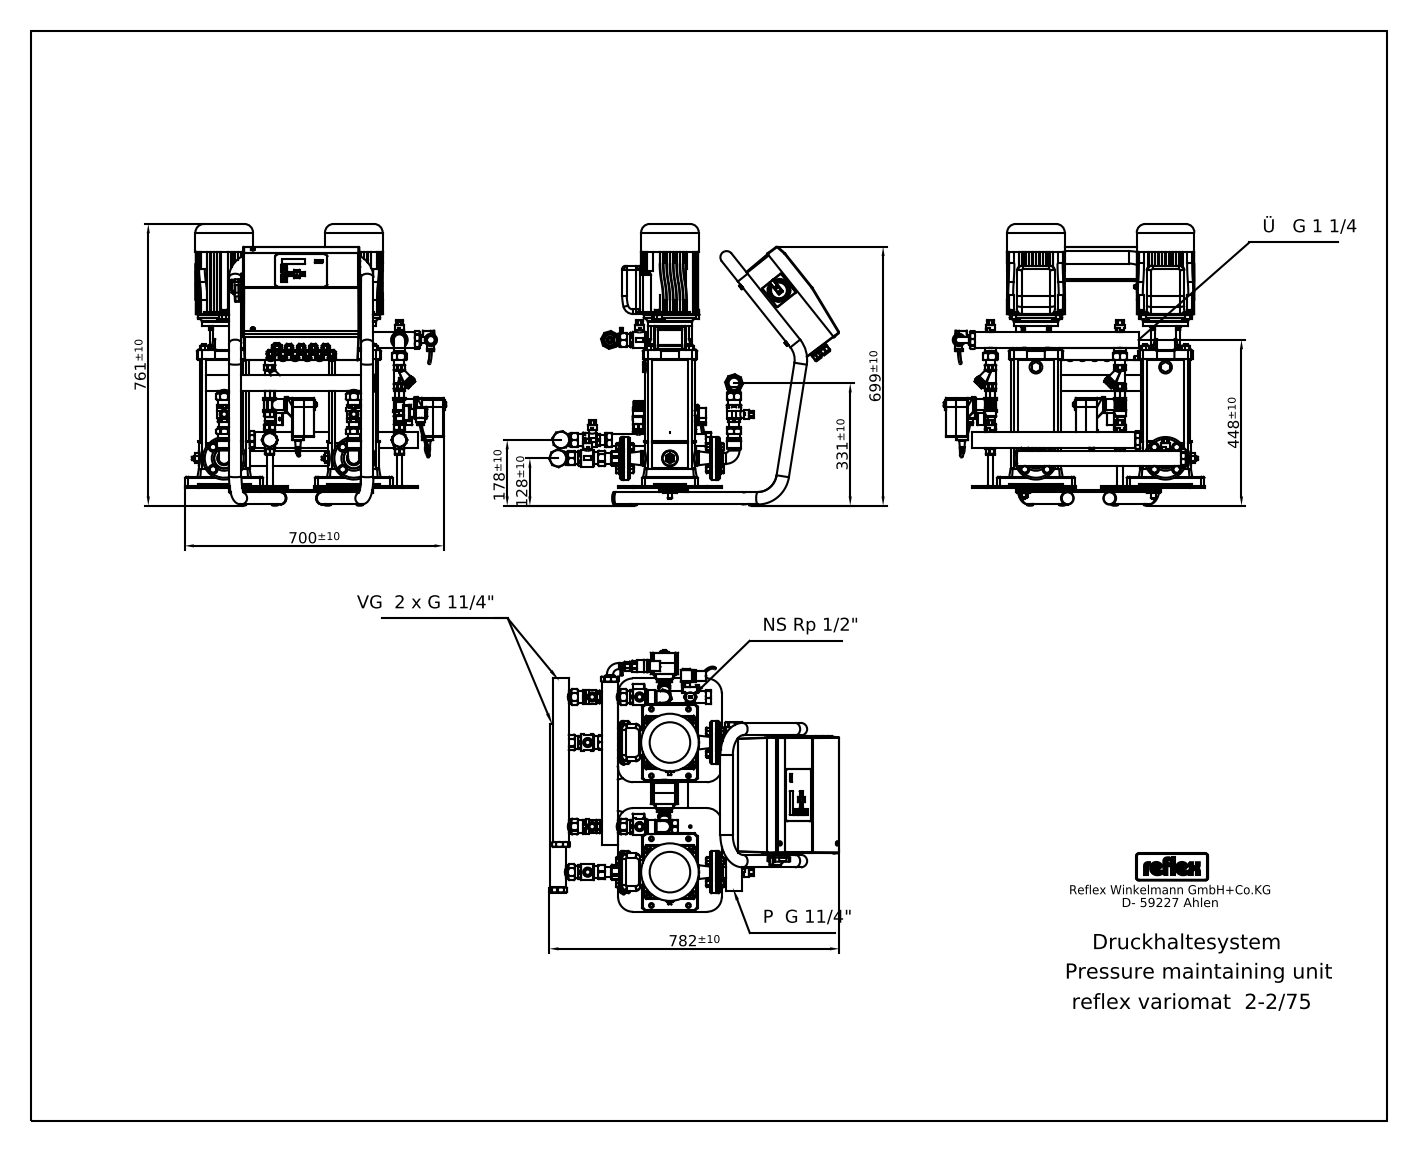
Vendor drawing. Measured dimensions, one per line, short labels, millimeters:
written by: Mechanical Desktop 2008 (CONFIG_CONTROL_DESIGN)
unit: mm
bodies: 97 solids, 3864 faces (2151 planar, 1405 cylindrical, 308 other)
size: 773.67 × 761 × 749.68
volume: 46 470 000 mm³; area: 3 681 000 mm²
holes: 11× ⌀10.5, 8× ⌀3, 8× ⌀6, 8× ⌀11, 8× ⌀14.5, 4× ⌀8, 2× ⌀27, 2× ⌀102, 1× ⌀6.5, 1× ⌀13.5, 1× ⌀45
bosses: 22× ⌀20, 14× ⌀33.7, 12× ⌀19, 10× ⌀17.5, 10× ⌀12, 9× ⌀30, 9× ⌀24.5, 8× ⌀20.6
rounds: 94× R280, 92× R278, 67× R1, 23× R5, 20× R10, 8× R10.5, 8× R25, 8× R40
face distances: 4, 2, 344, 29, 2.01, 6, 124, 350, 220, 373
hole spacings: 350, 32.07, 33, 56.63, 102.96, 66, 86.96, 99
